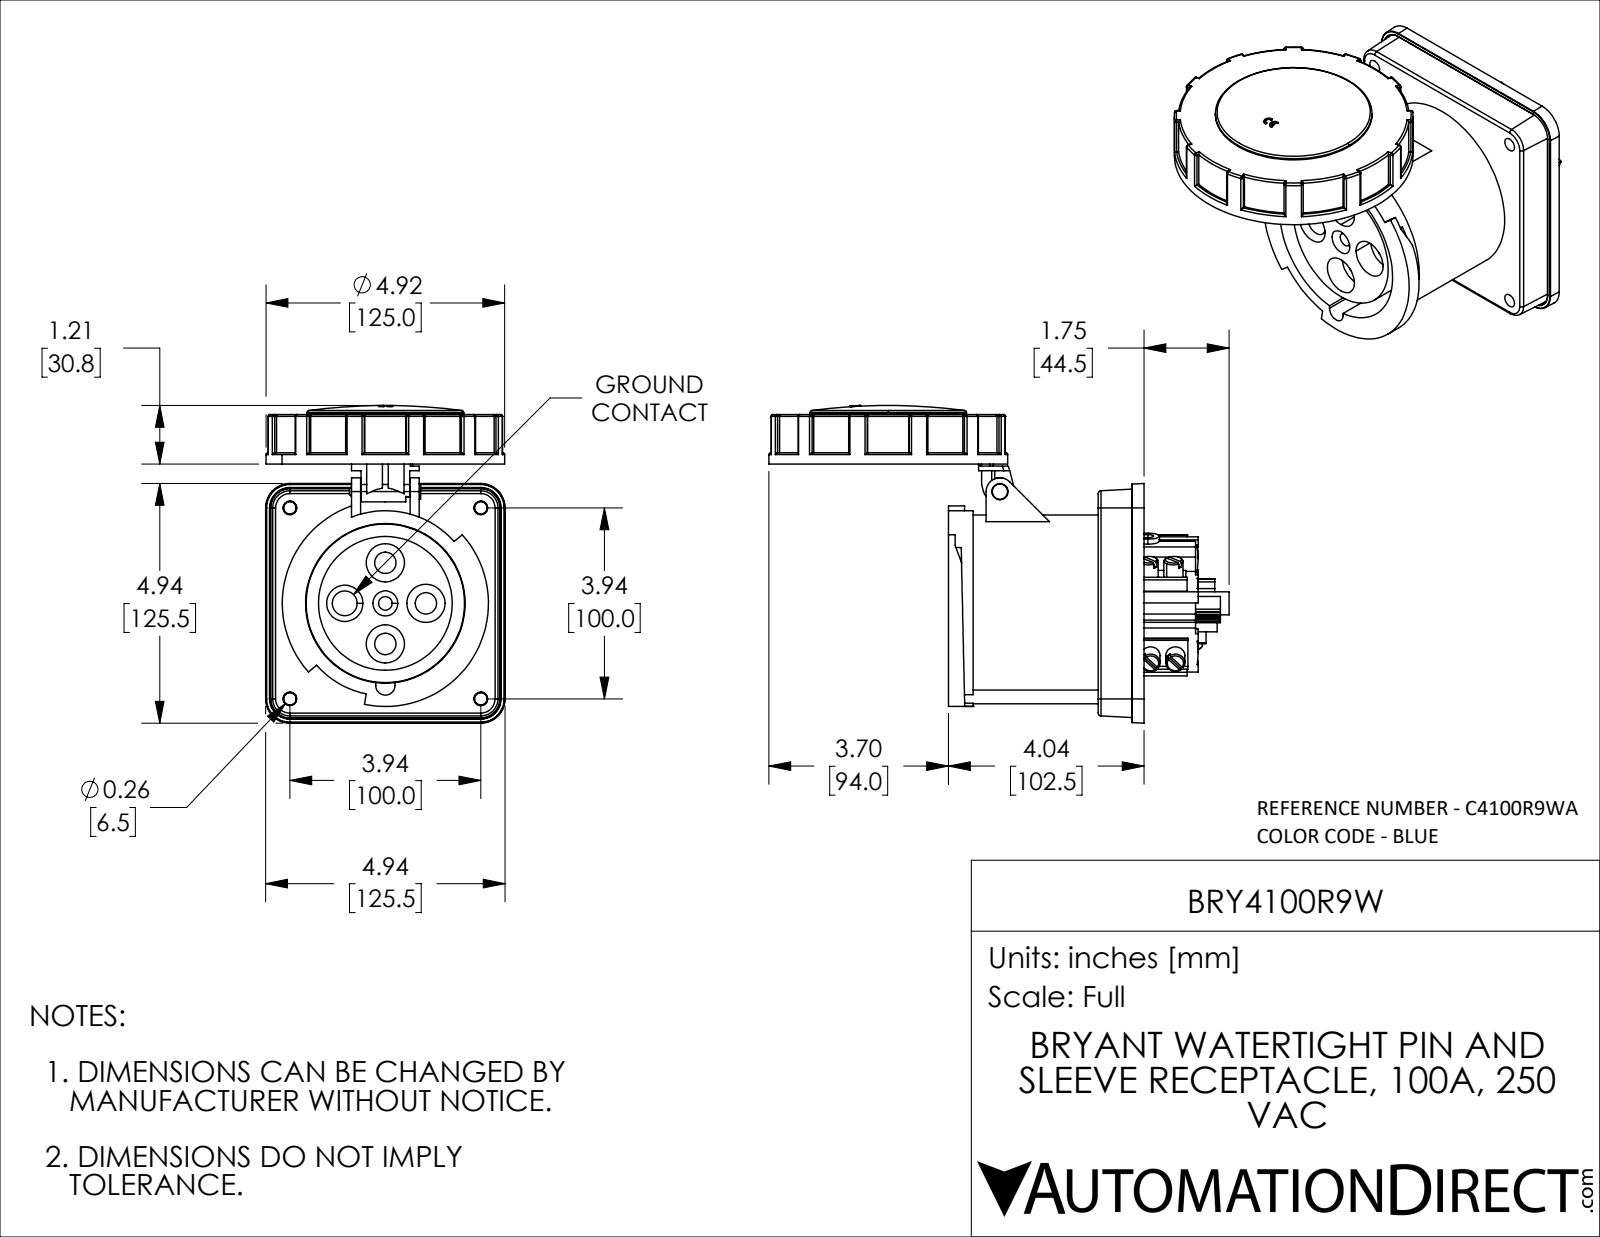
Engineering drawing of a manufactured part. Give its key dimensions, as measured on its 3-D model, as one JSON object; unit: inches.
{"part_name": "BRY4100R9W", "step_written_by": "SolidWorks 2021 (CONFIG_CONTROL_DESIGN)", "units": "inches", "bodies": {"solids": 2, "faces": 1003, "planar": 469, "cylindrical": 367, "other": 167}, "overall_size": [9.488, 6.551, 4.941], "volume_in3": 66.03, "surface_area_in2": 286.3, "round_holes": [[0.283, 4], [0.441, 3], [0.787, 3], [0.201, 1], [0.28, 1], [0.335, 1], [0.512, 1], [3.268, 1], [3.291, 1], [3.307, 1], [3.346, 1], [4.528, 1]], "round_bosses_or_shafts": [[0.394, 8], [4.921, 1], [3.819, 1], [3.646, 1], [3.228, 1], [3.169, 1], [2.756, 1], [0.472, 1]], "partial_cylinders_radius": [[0.039, 55], [0.079, 18], [0.098, 10], [0.01, 8], [0.118, 6], [0.197, 6], [0.02, 5], [0.059, 4]], "face_to_face_distances": [0.945, 1.024, 0.138, 4.035, 3.091, 0.079, 0.157, 0.787, 3.898, 2.953], "hole_center_spacings": [2.271, 3.427, 0.837, 1.183, 2.784, 3.937, 1.673, 5.568]}
